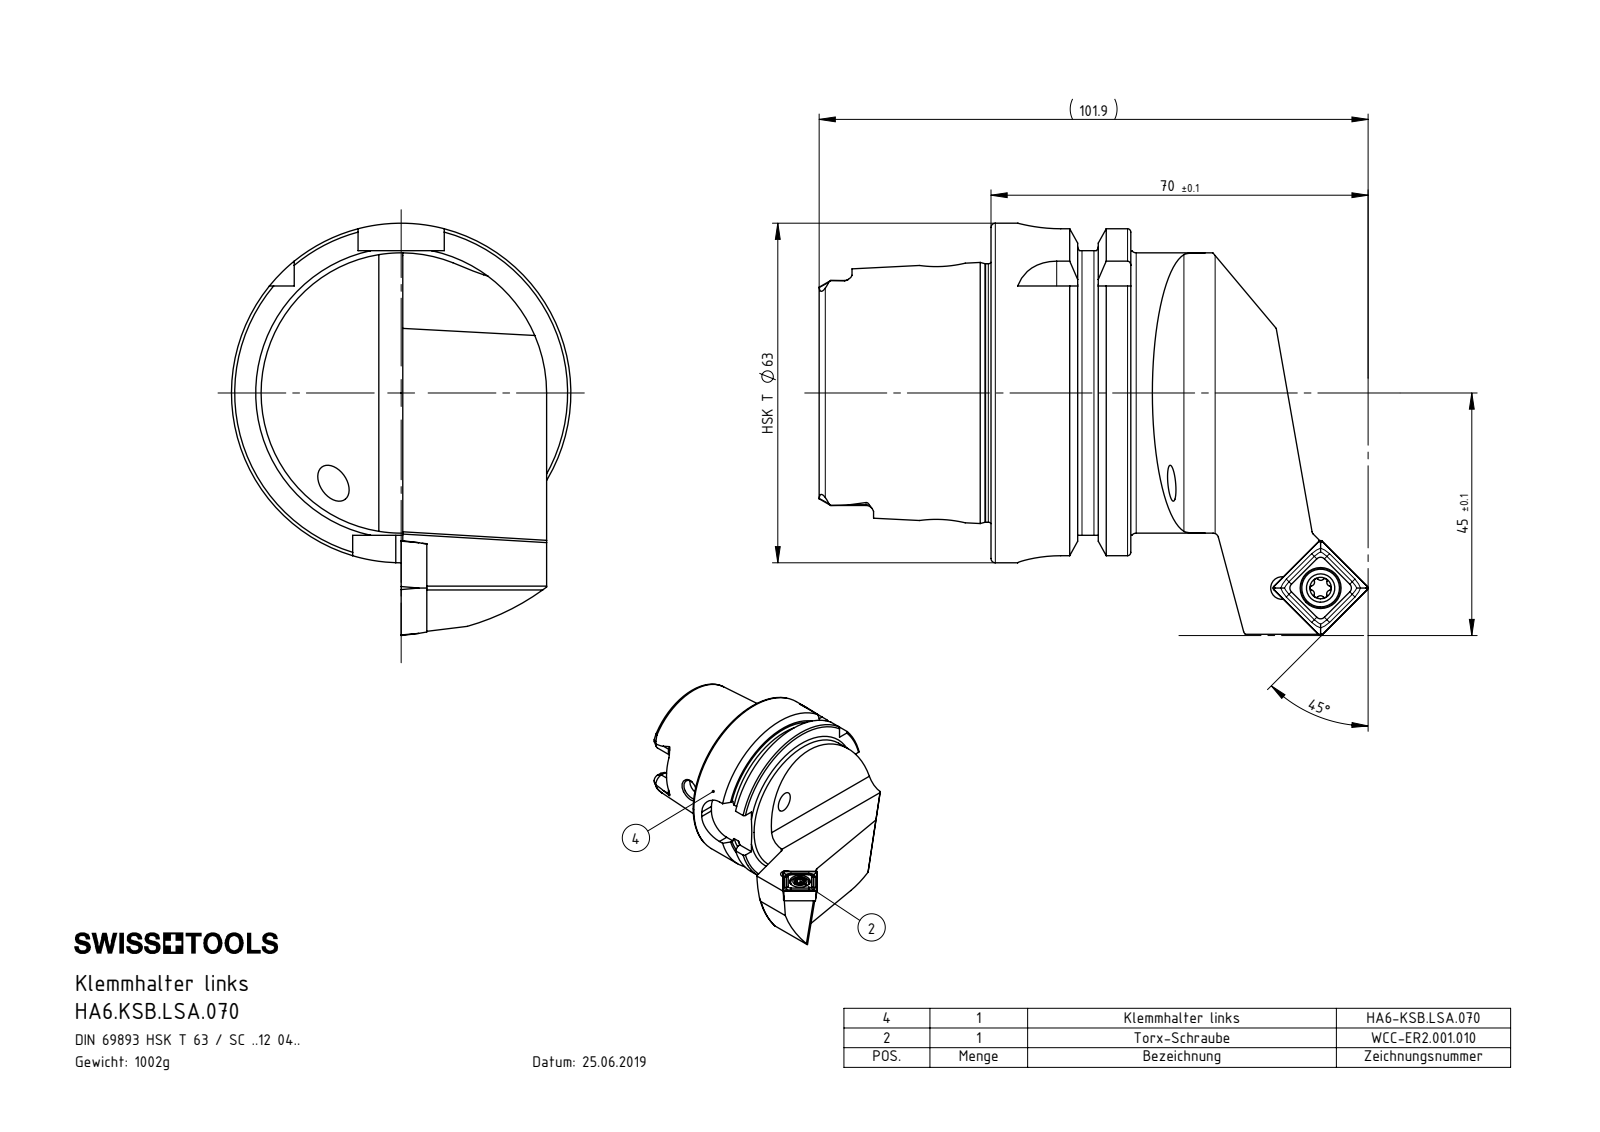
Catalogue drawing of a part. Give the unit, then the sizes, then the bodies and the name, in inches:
Units: inches
Overall size (bounding box): 4.012 × 3.012 × 2.48
Round holes (diameter × count): ⌀0.197 ×3, ⌀0.165 ×2, ⌀0.217 ×1, ⌀0.236 ×1, ⌀0.295 ×1, ⌀0.299 ×1, ⌀0.331 ×1, ⌀0.394 ×1, ⌀0.669 ×1, ⌀0.748 ×1, ⌀1.339 ×1, ⌀1.575 ×1
Round bosses / shafts (diameter × count): ⌀2.48 ×1, ⌀2.163 ×1, ⌀2.047 ×1, ⌀1.887 ×1, ⌀0.276 ×1, ⌀0.236 ×1, ⌀0.197 ×1
Partial cylindrical surfaces — rounded edges, fillets, slot ends (radius × count): R0.015 ×6, R0.055 ×6, R0.113 ×4, R0.315 ×4, R0.027 ×3, R0.027 ×3, R0.031 ×1, R0.236 ×1
Main face-to-face distances: 1.022, 0.63, 0.392, 1.051, 1.256, 1.648, 2.278, 0.876, 0.176, 2.079
Hole centre spacings: 0.278, 0.283, 2.336, 2.562, 2.565
Volume: 7.791 in³ · Surface area: 47.15 in²
Bodies: 6 solids, 328 faces (87 planar, 91 cylindrical, 150 other)
Part name (STEP PRODUCT): HA6.KSB.LSA.070; WCC-ER2.001.010_A; SCMT120404; HA6-KSB.LSA.070_A_Fertigbearbeitung (+1 more)
STEP written by: SolidWorks 2017 (AUTOMOTIVE_DESIGN)
